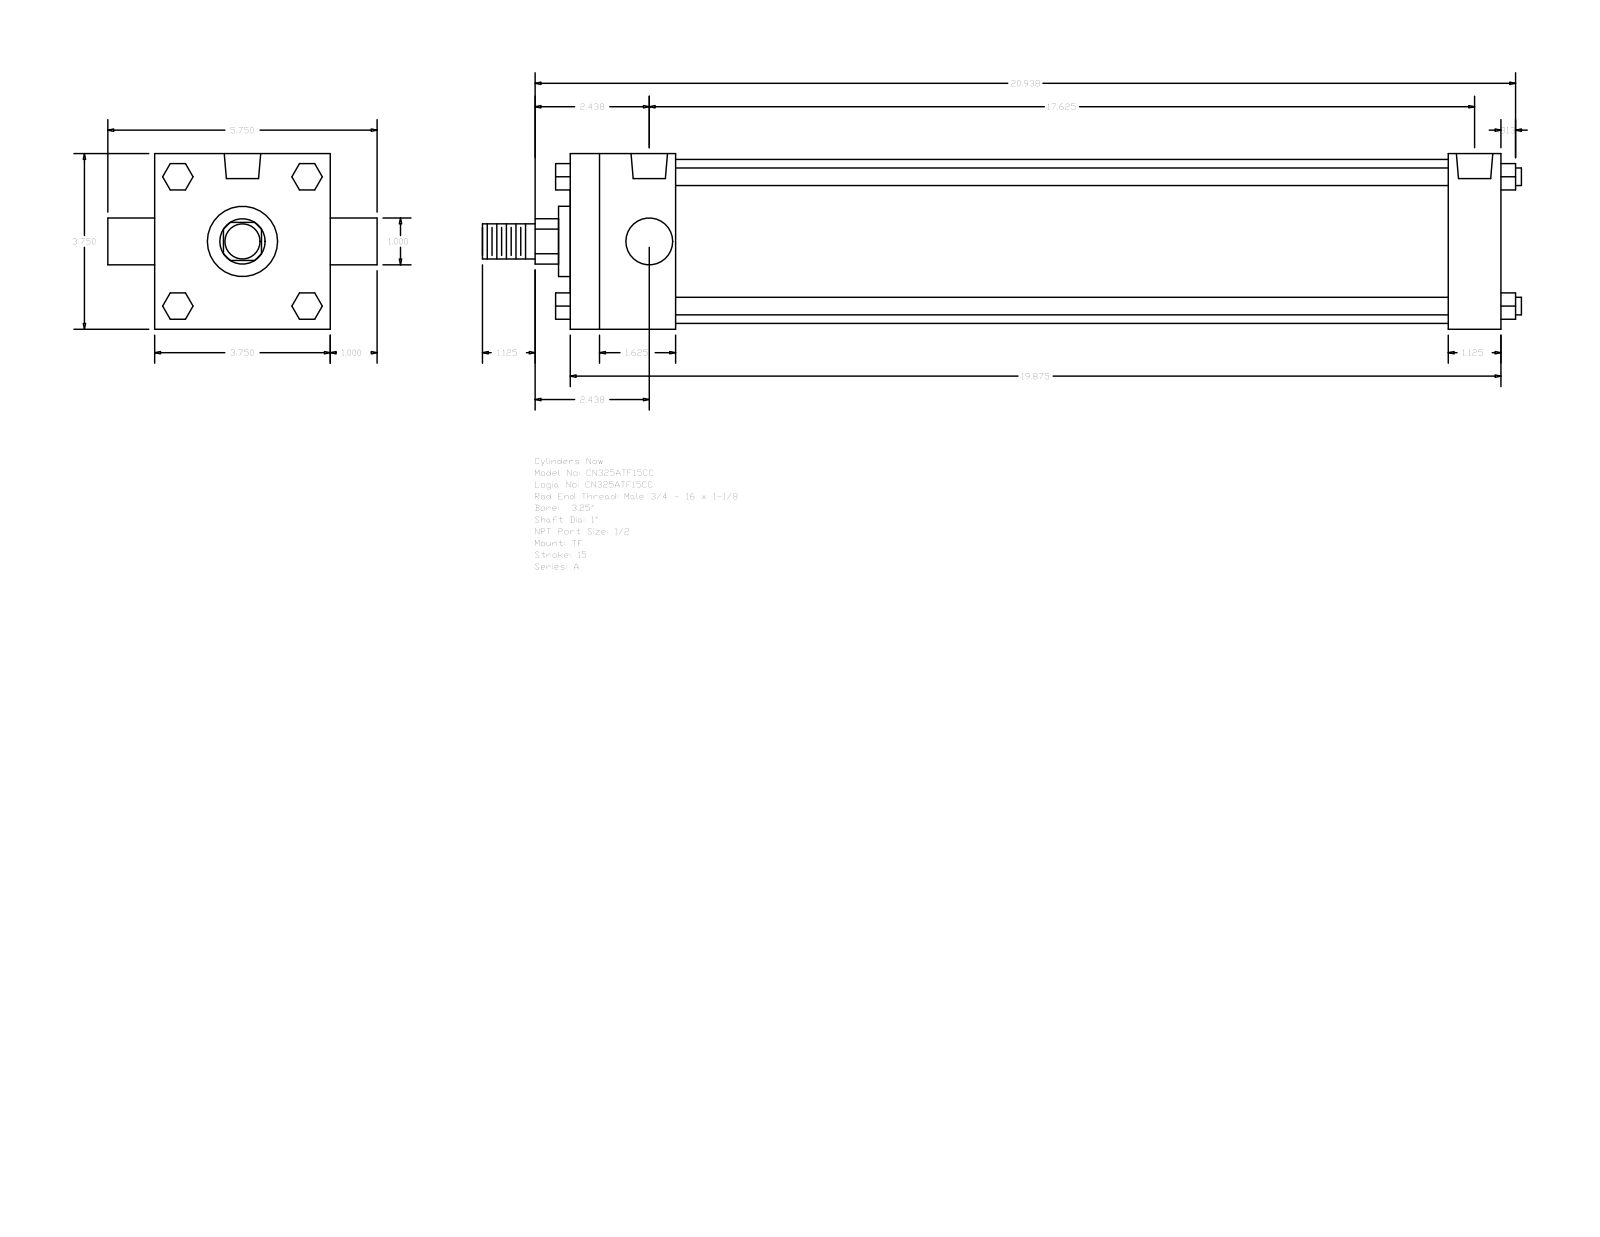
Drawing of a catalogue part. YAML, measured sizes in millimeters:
part_name: "A_TF__0325_1"
step_written_by: "GSSL Pune (CONFIG_CONTROL_DESIGN)"
units: millimeters
bodies: {solids: 0, faces: 120, planar: 92, cylindrical: 28, other: 0}
overall_size: [563.56, 146.05, 95.25]
round_holes:
  - {diameter: 8.73, count: 3}
  - {diameter: 19.77, count: 2}
round_bosses_or_shafts:
  - {diameter: 9.53, count: 4}
  - {diameter: 25.4, count: 2}
  - {diameter: 88.9, count: 1}
  - {diameter: 38.1, count: 1}
  - {diameter: 19.05, count: 1}
partial_cylinders:
  - {radius: 12.29, count: 1}
face_to_face_distances: [95.24, 504.83, 57.15, 476.25, 419.1, 447.68, 28.58, 14.28, 35.05, 60.71]
hole_center_spacings: [3.18, 444.5, 441.32, 447.68]
